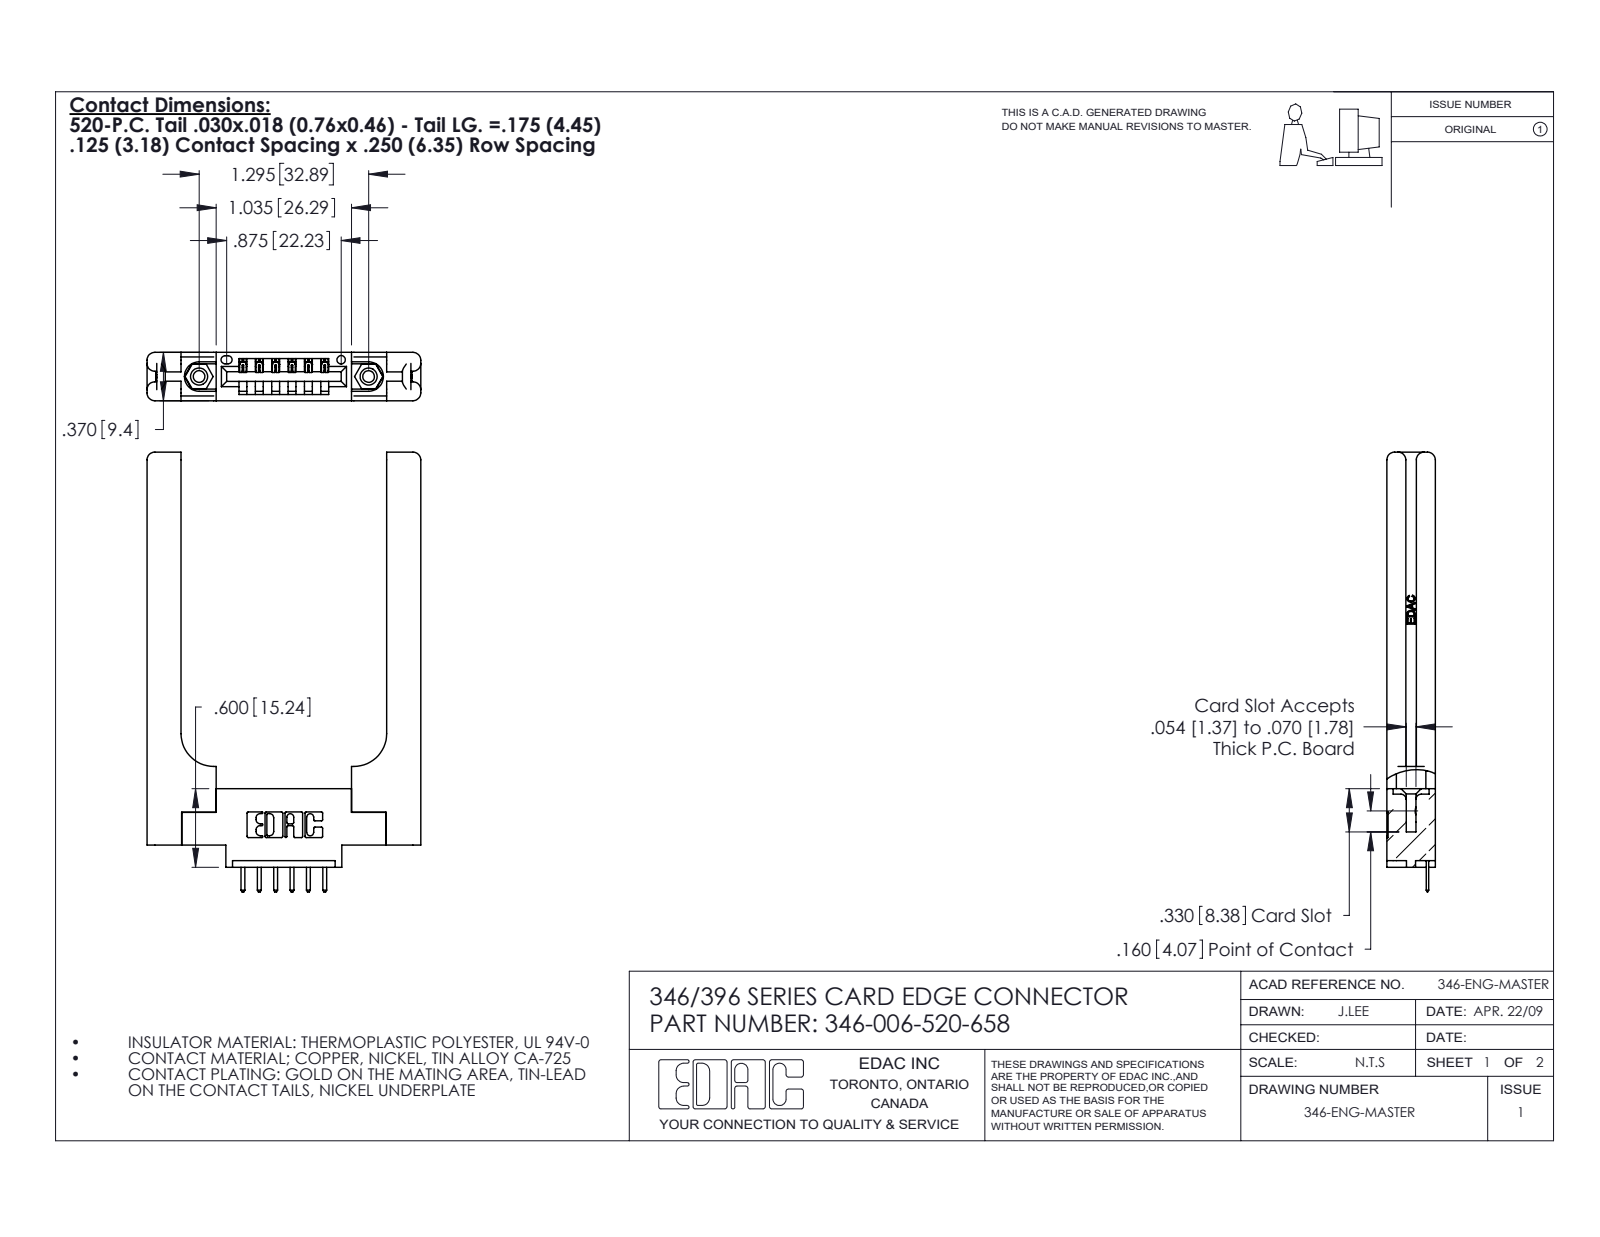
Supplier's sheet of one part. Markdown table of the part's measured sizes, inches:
| quantity | value |
| --- | --- |
| part name | 346-006-520-658; 345-250-001_345-250-001-102; 346 Part_0.170 Offset - 0.156 Dia-TH; 346-220-058_345-220-058 (+1 more) |
| STEP written by | SolidWorks 2020 (CONFIG_CONTROL_DESIGN) |
| units | inches |
| bodies | 11 solids, 768 faces (494 planar, 214 cylindrical, 60 other) |
| overall size | 3.358 × 2.091 × 0.37 |
| volume | 0.742 in³ |
| surface area | 16.62 in² |
| round holes (diameter × count) | 0.089 × 2, 0.125 × 2, 0.156 × 2, 0.064 × 1 |
| round bosses / shafts (diameter × count) | 0.155 × 2 |
| partial cylindrical surfaces (radius × count) | 0.01 × 22, 0.06 × 16, 0.01 × 14, 0.006 × 12, 0.007 × 6, 0.031 × 6, 0.026 × 3, 0.03 × 2 |
| main face-to-face distances | 0.37, 0.15, 0.22, 0.072, 0.25, 1.571, 0.148, 0.071, 0.12, 0.048 |
| hole center spacings | 0.246, 1.092, 1.295 |
